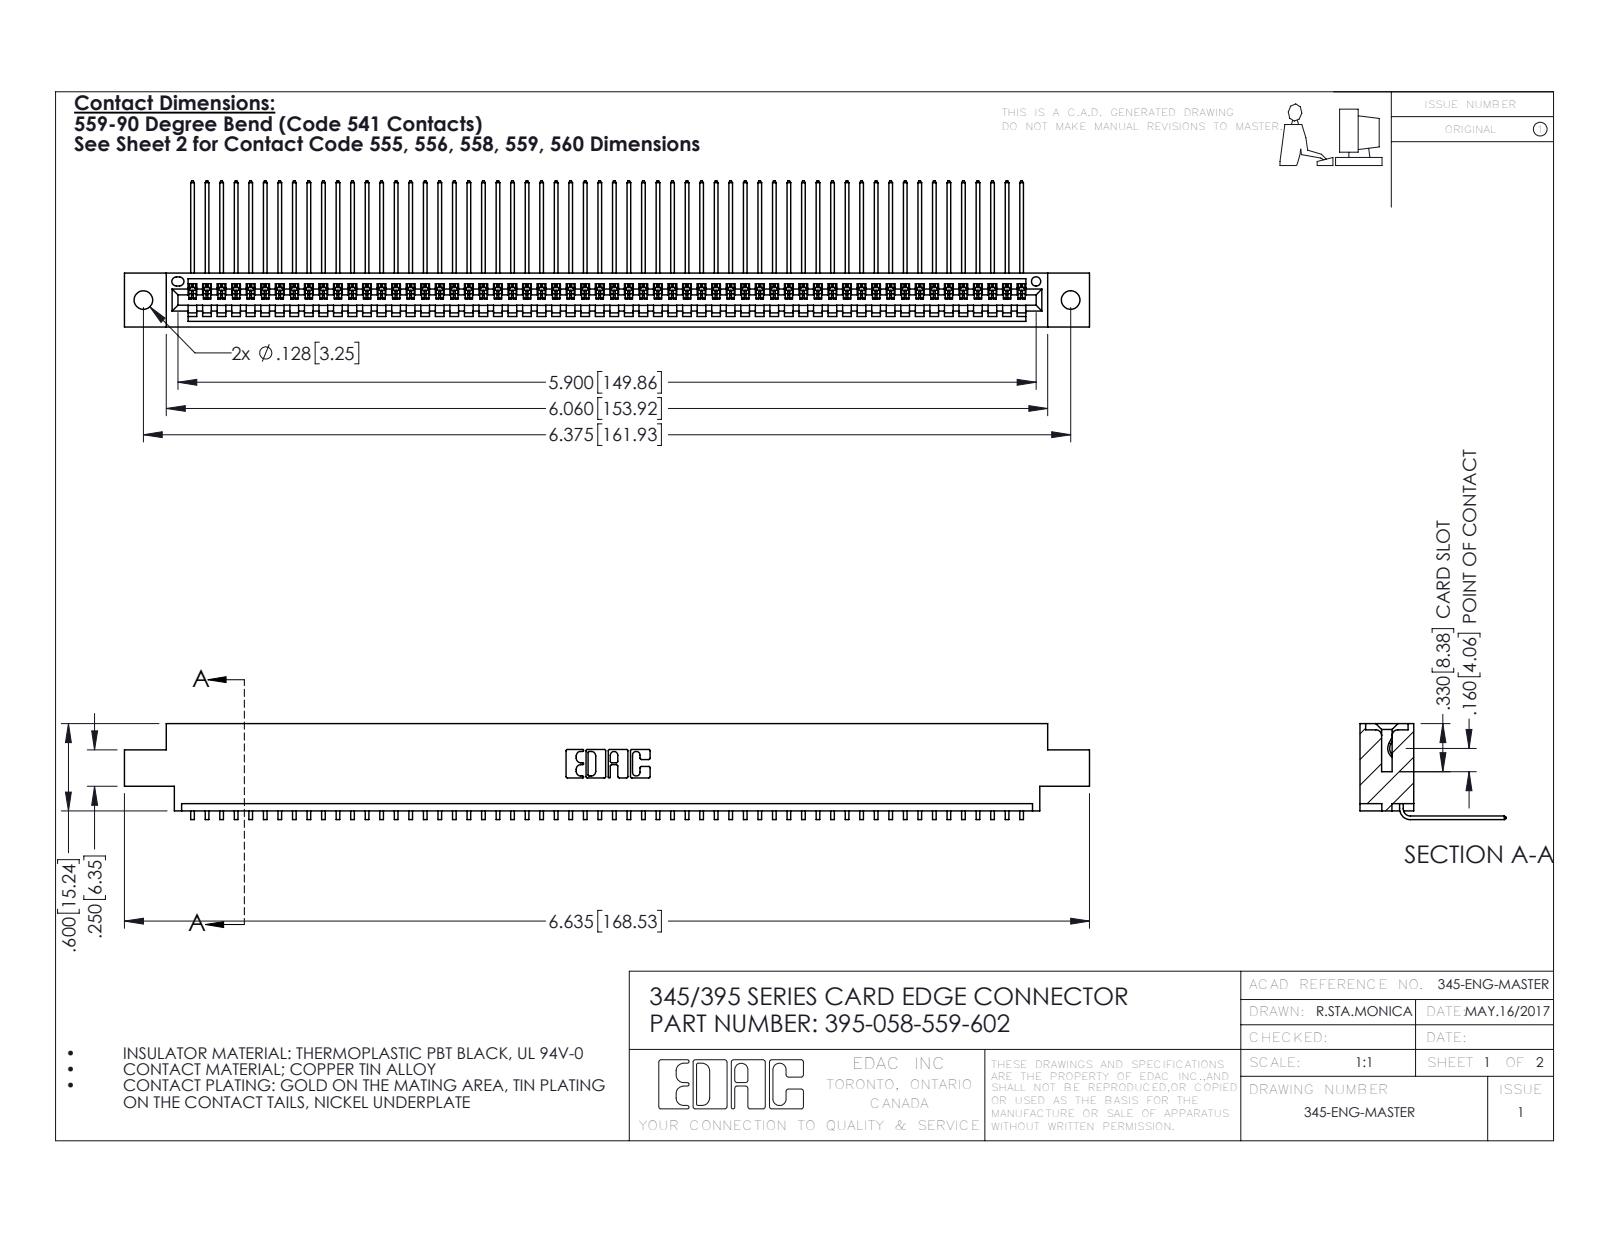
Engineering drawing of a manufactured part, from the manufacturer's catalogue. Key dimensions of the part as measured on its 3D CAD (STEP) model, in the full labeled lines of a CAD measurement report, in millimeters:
Part name (STEP PRODUCT): 345 Part_0.170 Offset - 0.128 Dia; 345-292-001_558 559 Tail - 1; 395-058-559-602
STEP written by: SolidWorks 2016 (CONFIG_CONTROL_DESIGN)
Units: millimetres
Bodies: 59 solids, 3610 faces (2520 planar, 1090 cylindrical, 0 other)
Overall size (bounding box): 168.5 × 25.5 × 16.7
Volume: 16 200 mm³ · Surface area: 22 710 mm²
Round holes (diameter × count): ⌀3.3 ×2, ⌀1.6 ×1
Partial cylindrical surfaces — rounded edges, fillets, slot ends (radius × count): R0.2 ×116, R0.3 ×22, R0.2 ×6, R0.8 ×6, R0.7 ×3, R0.8 ×2, R1 ×2, R0.4 ×1
Main face-to-face distances: 1.8, 7.6, 9.4, 5.1, 2.5, 6.9, 0.6, 5.7, 4.4, 3.8
Hole centre spacings: 6.9, 155.9, 161.9
